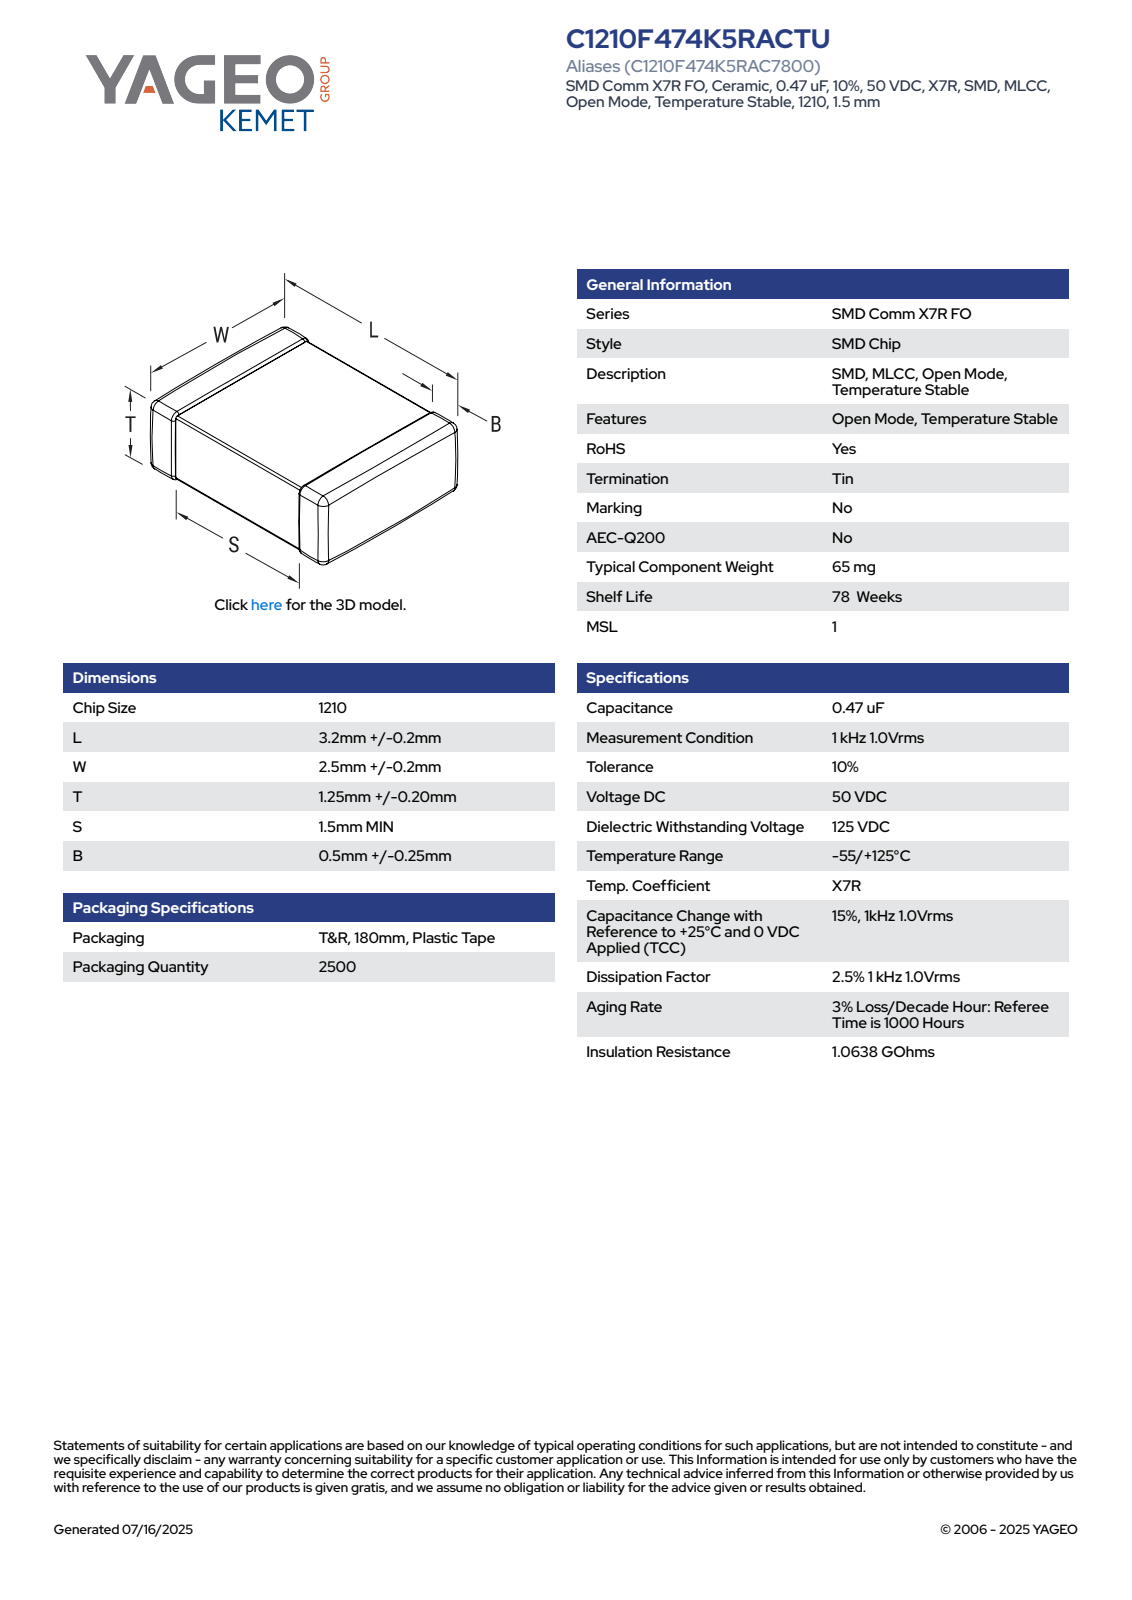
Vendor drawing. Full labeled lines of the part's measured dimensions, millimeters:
Part name (STEP PRODUCT): CCS_CCSTD_1210_L3.4W2.7T1.45B0.5
STEP written by: SolidWorks 2021 (AUTOMOTIVE_DESIGN)
Units: millimetres
Bodies: 4 solids, 125 faces (71 planar, 38 cylindrical, 16 other)
Overall size (bounding box): 3.4 × 2.7 × 1.45
Volume: 12 mm³ · Surface area: 36 mm²
Main face-to-face distances: 1.39, 1.33, 3.4, 2.64, 1.45, 2.58, 2.7, 1.4, 1.34, 0.4
